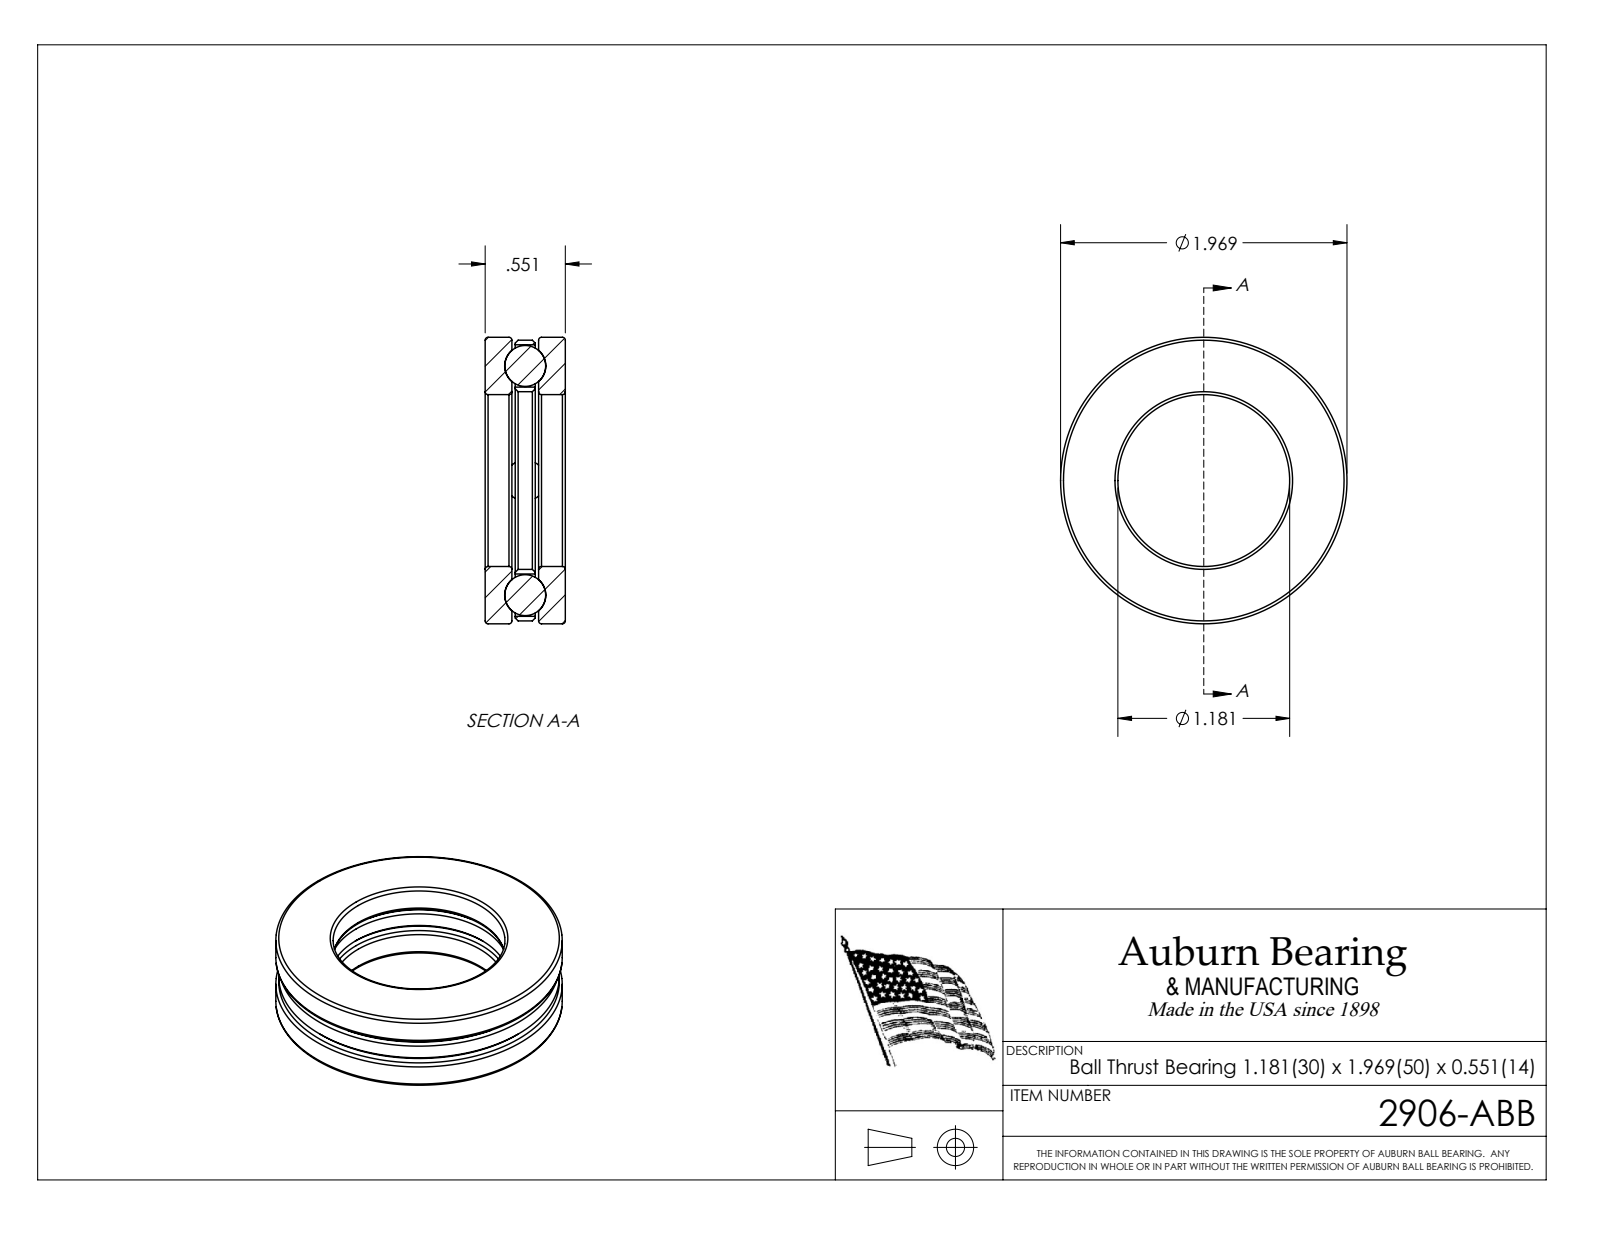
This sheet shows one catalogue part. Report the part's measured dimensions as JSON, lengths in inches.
{"part_name": "2906-ABB", "step_written_by": "SolidWorks 2017 (CONFIG_CONTROL_DESIGN)", "units": "inches", "bodies": {"solids": 7, "faces": 36, "planar": 8, "cylindrical": 10, "other": 18}, "overall_size": [1.969, 1.969, 0.551], "volume_in3": 0.889, "surface_area_in2": 16.97, "round_holes": [[0.291, 4], [1.181, 1], [1.221, 1]], "round_bosses_or_shafts": [[1.969, 1], [1.929, 1]], "face_to_face_distances": [0.207, 0.344, 0.551, 0.184, 0.367, 0.023, 0.161, 0.138, 0.183], "hole_center_spacings": [0.787, 1.113, 1.575]}
